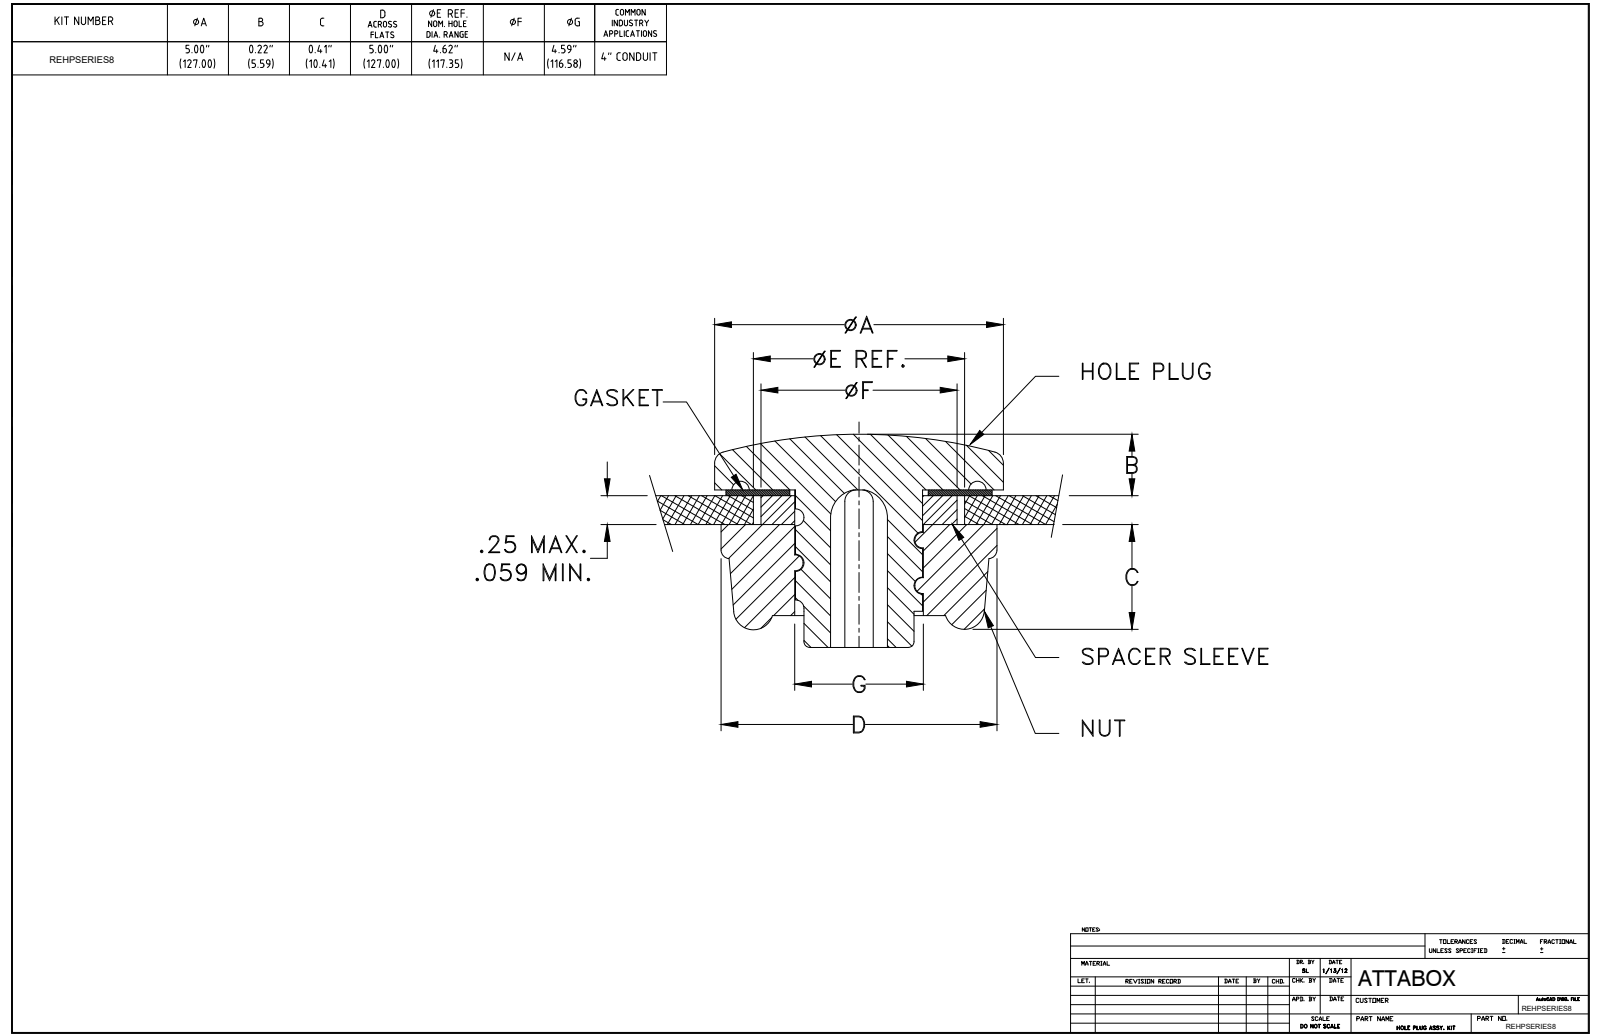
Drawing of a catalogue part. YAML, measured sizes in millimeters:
part_name: "HPSERIES8"
step_written_by: "SolidWorks 2018 (AUTOMOTIVE_DESIGN)"
units: millimeters
bodies: {solids: 3, faces: 167, planar: 37, cylindrical: 59, other: 71}
overall_size: [141.3, 132.7, 28.7]
volume: 211200
surface_area: 57850
round_holes:
  - {diameter: 116.6, count: 1}
  - {diameter: 117.1, count: 1}
round_bosses_or_shafts:
  - {diameter: 127, count: 1}
  - {diameter: 126, count: 1}
  - {diameter: 124, count: 1}
  - {diameter: 115.1, count: 1}
partial_cylinders:
  - {radius: 0.2, count: 8}
  - {radius: 0.3, count: 8}
  - {radius: 1, count: 8}
  - {radius: 2, count: 8}
  - {radius: 0.8, count: 6}
  - {radius: 15, count: 6}
  - {radius: 4.4, count: 2}
face_to_face_distances: [19.1, 12.9, 6.2, 18.3, 5.4, 0.8, 16, 3.2, 2.3, 3]
